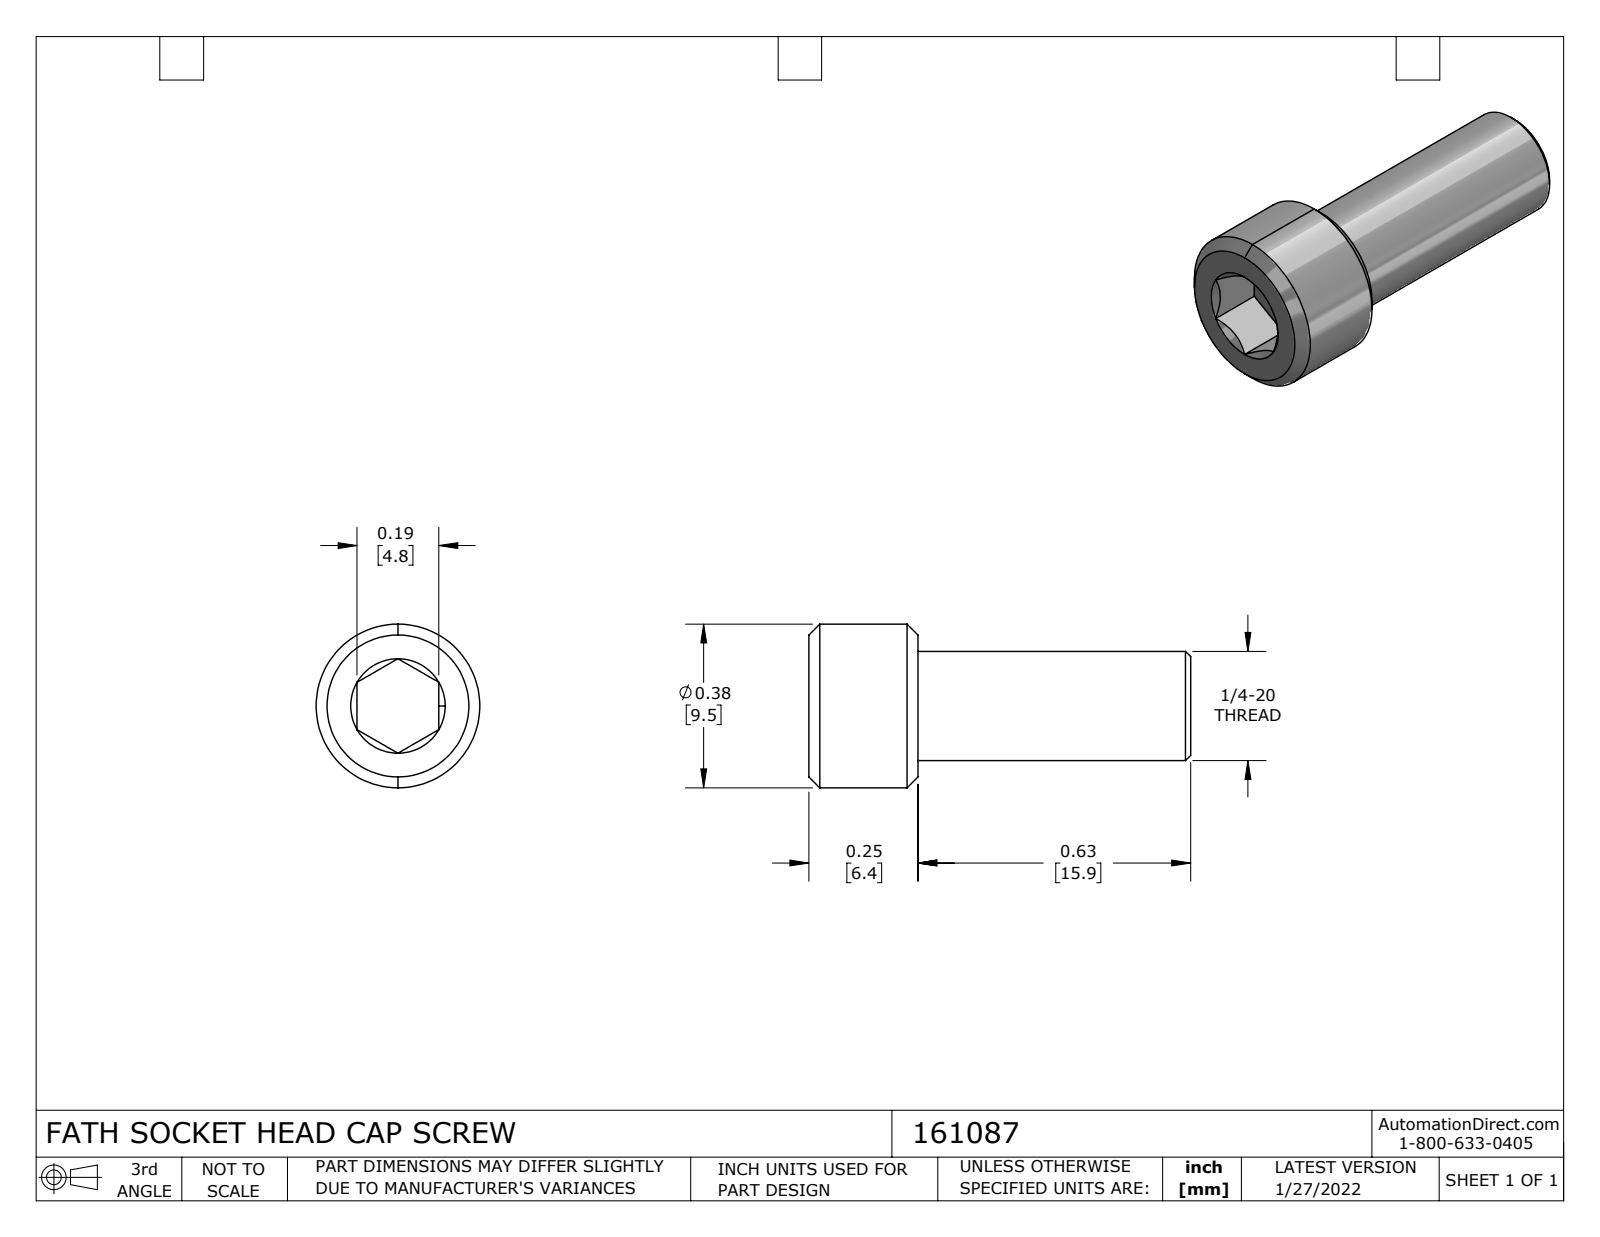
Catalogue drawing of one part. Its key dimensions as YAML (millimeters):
part_name: "161087"
step_written_by: "SolidWorks 2021 (CONFIG_CONTROL_DESIGN)"
units: millimeters
bodies: {solids: 1, faces: 27, planar: 10, cylindrical: 4, other: 13}
overall_size: [22.2, 9.5, 9.5]
volume: 880
surface_area: 672
round_bosses_or_shafts:
  - {diameter: 9.5, count: 1}
  - {diameter: 6.4, count: 1}
face_to_face_distances: [22.2, 4.7, 15.9, 6.4, 19.1, 3.2, 3.2]
